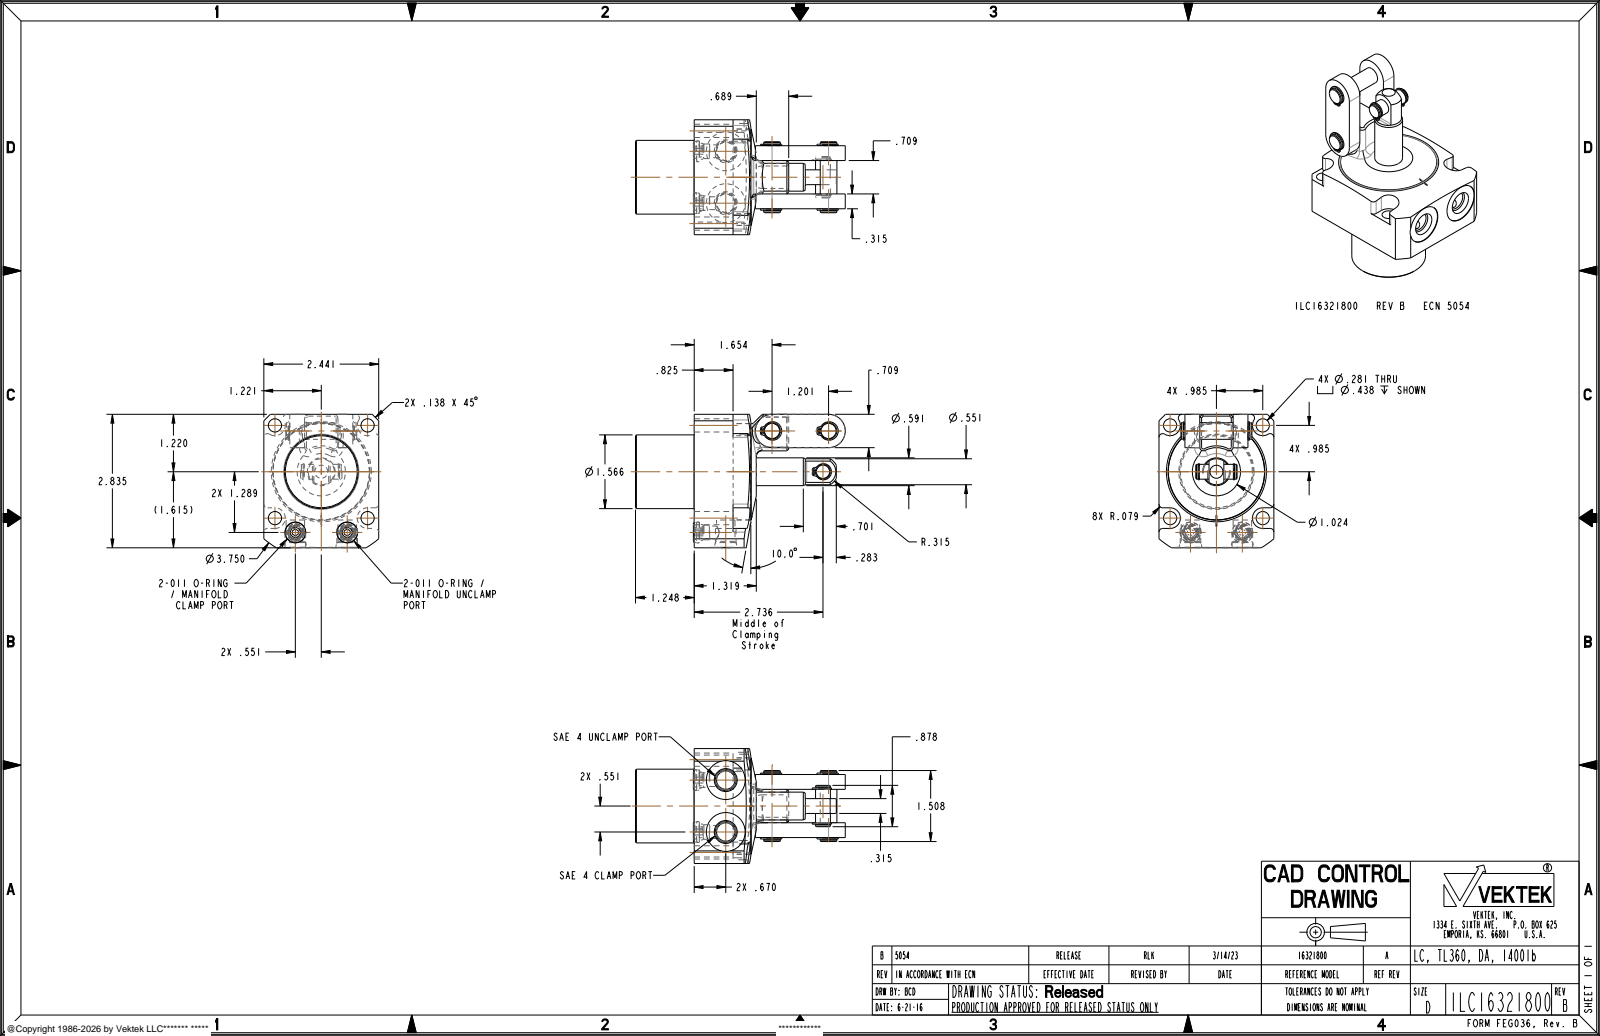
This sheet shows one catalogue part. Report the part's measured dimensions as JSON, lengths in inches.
{"part_name": "ILC16321800_BODY; ILC16321800_LUG; ILC16321800", "step_written_by": "CREO PARAMETRIC BY PTC INC, 2021164 (AUTOMOTIVE_DESIGN)", "units": "inches", "bodies": {"solids": 2, "faces": 380, "planar": 130, "cylindrical": 173, "other": 77}, "overall_size": [4.458, 2.836, 2.441], "volume_in3": 11.78, "surface_area_in2": 64.06, "round_holes": [[0.041, 6], [0.281, 4], [0.272, 2], [0.392, 2], [0.443, 2], [0.825, 2], [2.048, 1]], "round_bosses_or_shafts": [[0.437, 2], [0.43, 2], [0.393, 2], [0.354, 2], [0.33, 2], [0.31, 2], [0.236, 2], [0.21, 2]], "partial_cylinders_radius": [[0.079, 10], [0.041, 6], [0.031, 4], [0.069, 4], [0.219, 4], [0.091, 2], [0.354, 2], [0.172, 1]], "face_to_face_distances": [0.827, 2.441, 0.551, 1.89, 1.248, 2.075, 0.866, 1.575, 0.315, 1.024], "hole_center_spacings": [1.393, 1.969, 0.092, 0.53, 1.102, 1.201, 1.204, 1.401]}
